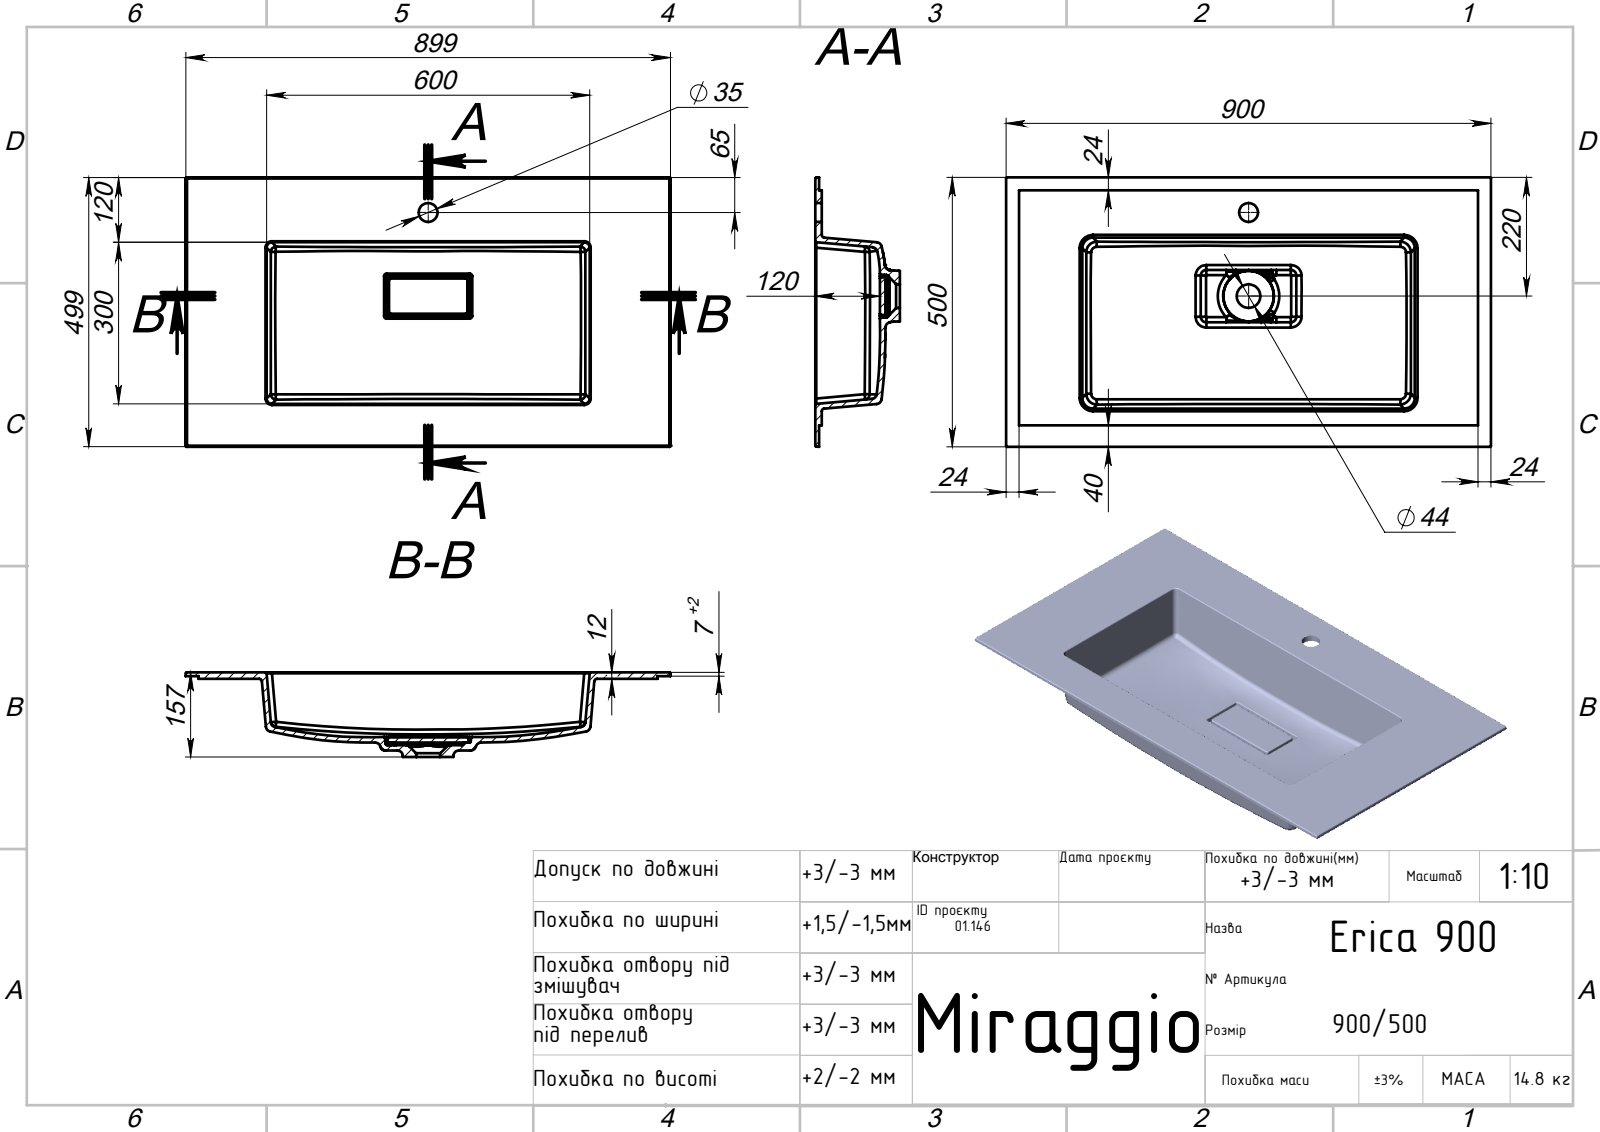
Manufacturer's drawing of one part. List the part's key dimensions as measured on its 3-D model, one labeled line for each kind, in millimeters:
Part name (STEP PRODUCT): Erica 900
STEP written by: SolidWorks 2020 (AUTOMOTIVE_DESIGN)
Units: millimetres
Bodies: 2 solids, 244 faces (44 planar, 69 cylindrical, 131 other)
Overall size (bounding box): 900 × 500 × 157
Volume: 6 605 000 mm³ · Surface area: 1 292 000 mm²
Round holes (diameter × count): ⌀35 ×1
Partial cylindrical surfaces — rounded edges, fillets, slot ends (radius × count): R2 ×27, R3 ×19, R6 ×6, R5 ×4, R10 ×4, R20 ×4
Main face-to-face distances: 12, 10, 5, 7, 9.99, 123, 118, 130, 108, 113
